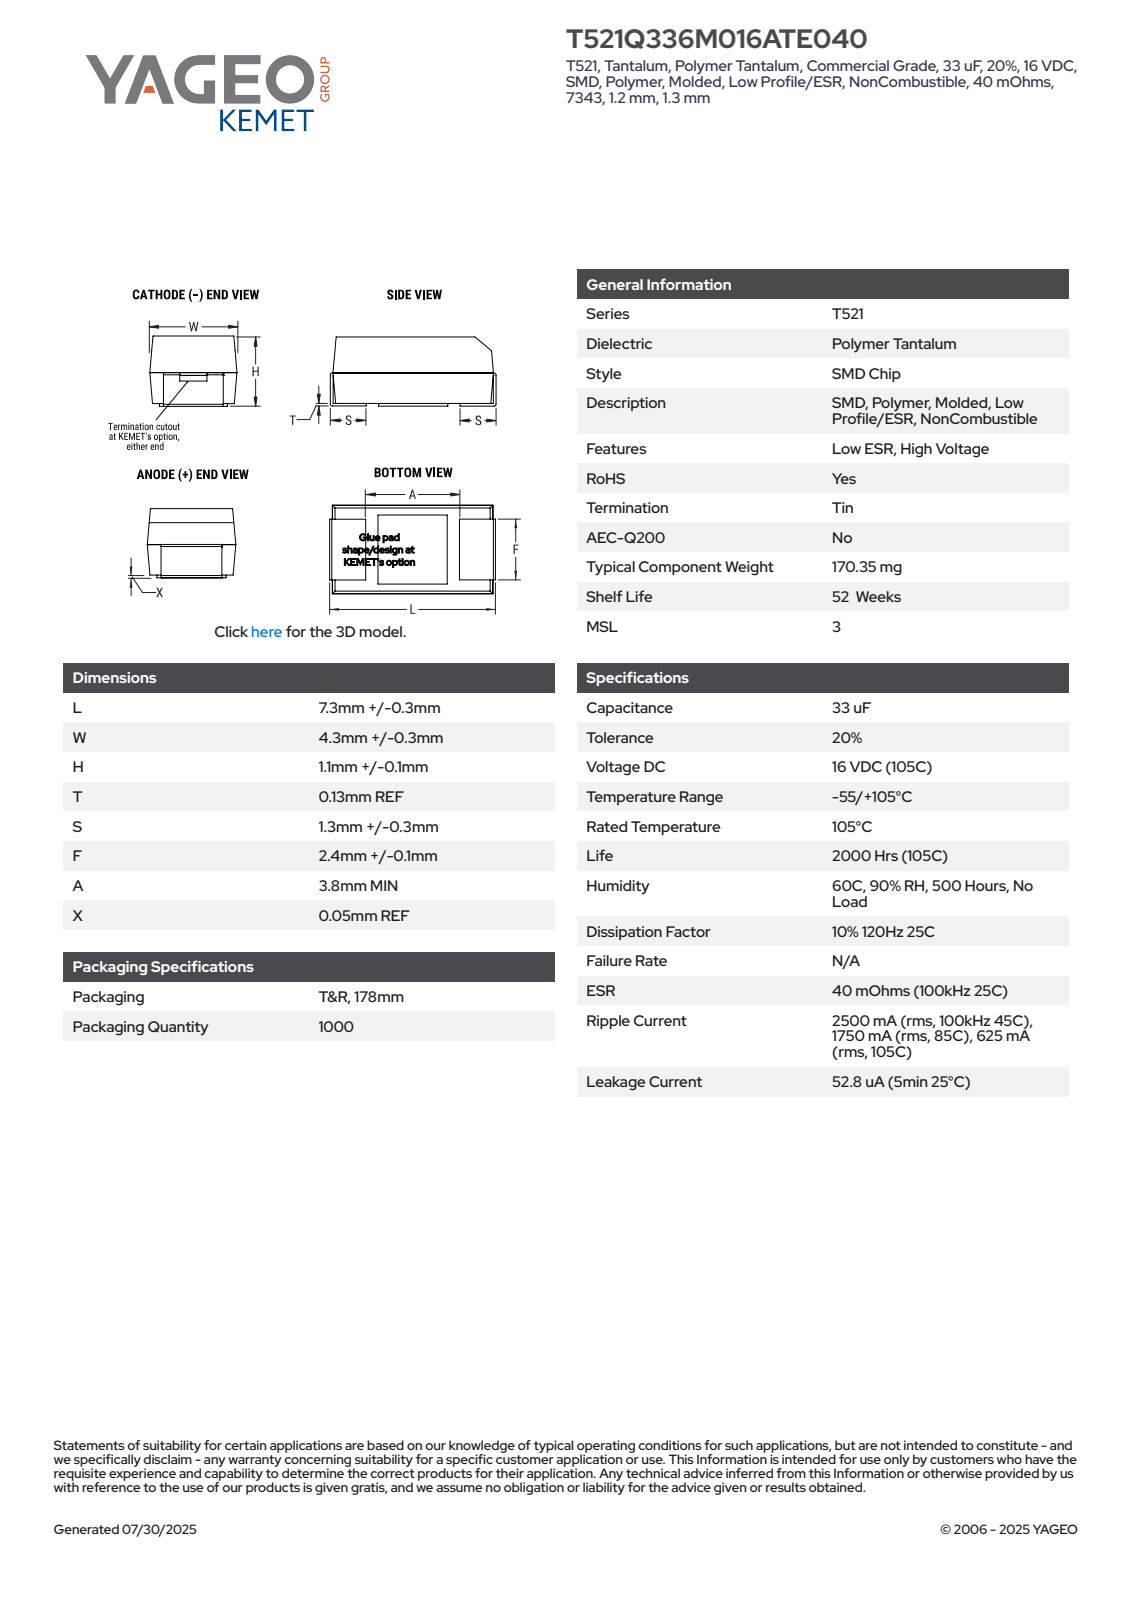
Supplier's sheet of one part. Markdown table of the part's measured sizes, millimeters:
| quantity | value |
| --- | --- |
| part name | CTSM_TCM2NBKRPEG_7343_L7.6W4.6H1.2T0.13S1.3F2.5A3.8X0.05 |
| STEP written by | SolidWorks 2014 (AUTOMOTIVE_DESIGN) |
| units | millimeters |
| bodies | 4 solids, 90 faces (86 planar, 4 cylindrical, 0 other) |
| overall size | 7.6 × 4.6 × 1.33 |
| volume | 38 mm³ |
| surface area | 96 mm² |
| partial cylindrical surfaces (radius × count) | 0.1 × 4 |
| main face-to-face distances | 1.2, 4.21, 1.33, 7.47, 7.6, 7.34, 1.3, 6.3, 1.17, 6.17 |
